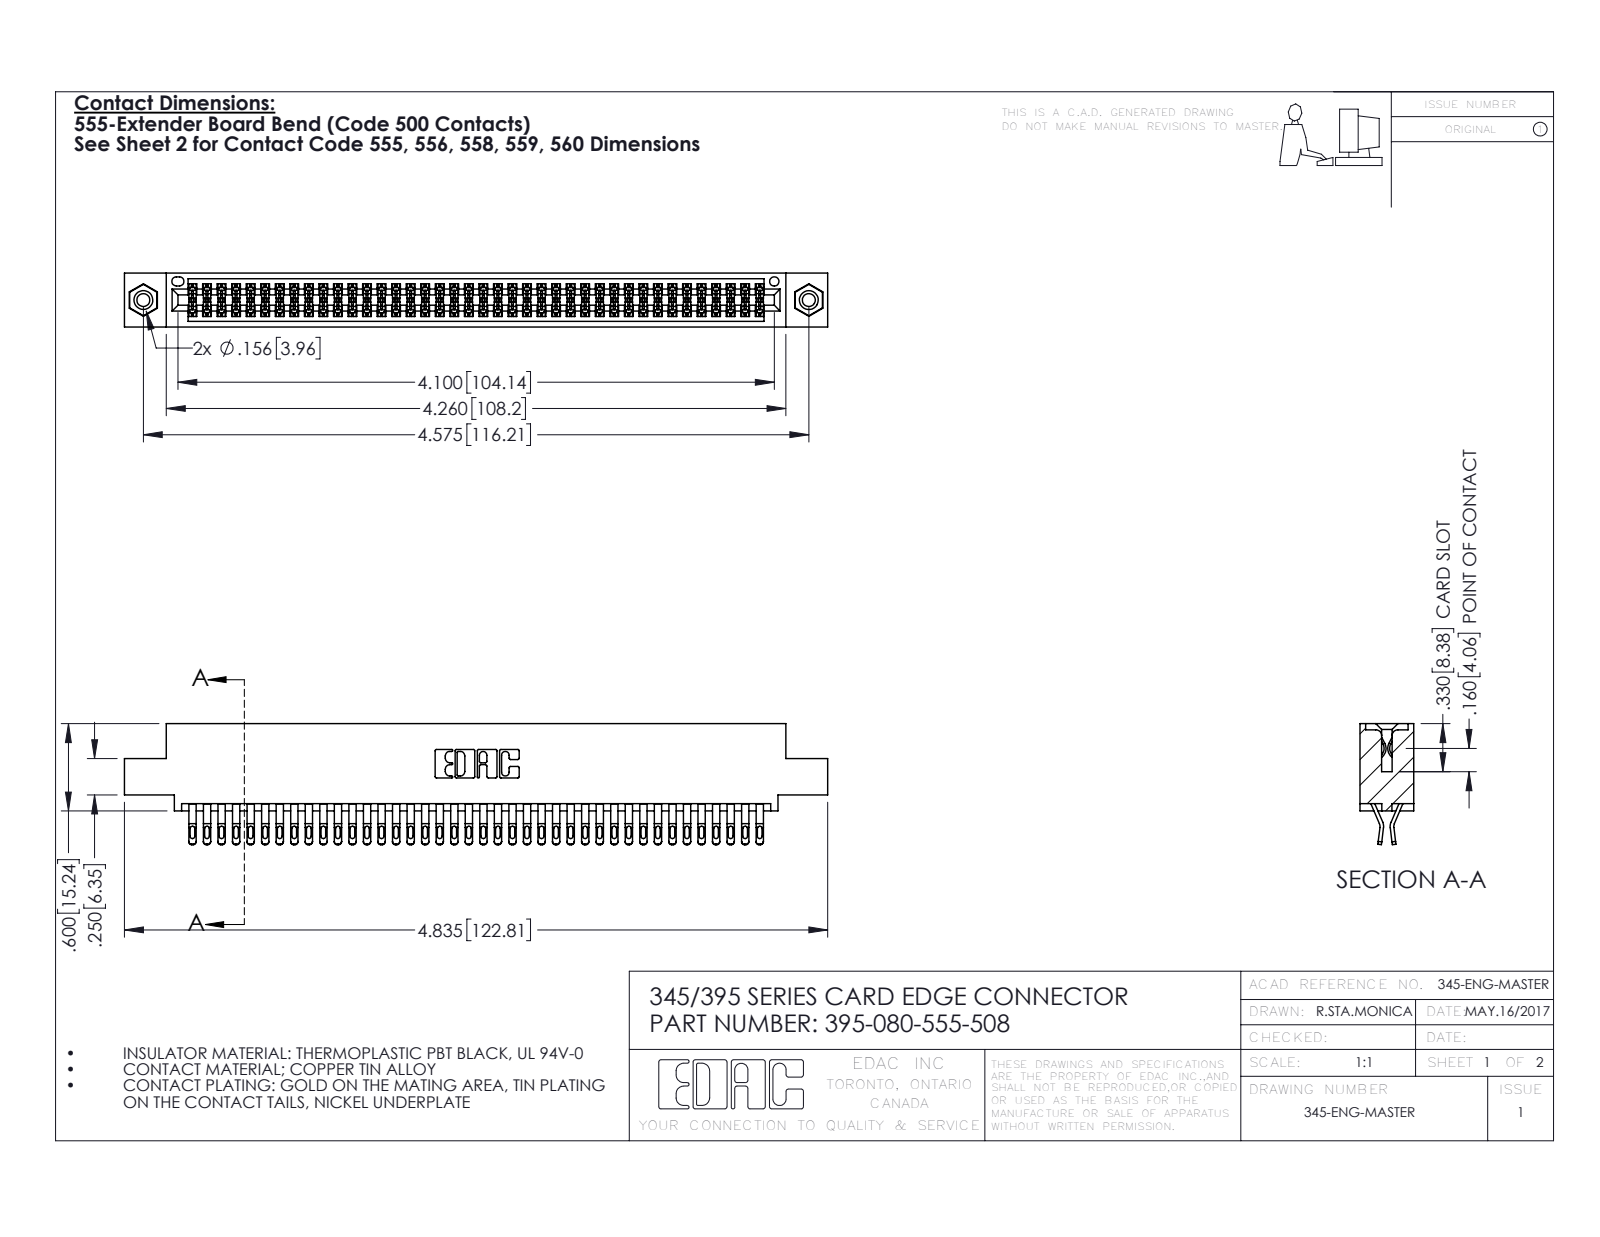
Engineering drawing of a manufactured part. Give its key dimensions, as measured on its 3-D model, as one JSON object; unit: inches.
{"part_name": "345-250-001_345-250-003-102; 345-292-001_555 Tail; 395-080-555-508; 345 Part_0.110 Offset - 0.156 Dia-TI", "step_written_by": "SolidWorks 2016 (CONFIG_CONTROL_DESIGN)", "units": "inches", "bodies": {"solids": 83, "faces": 4670, "planar": 2596, "cylindrical": 2058, "other": 16}, "overall_size": [4.835, 0.832, 0.37], "volume_in3": 0.736, "surface_area_in2": 28.99, "round_holes": [[0.089, 2], [0.125, 2], [0.156, 2], [0.064, 1]], "round_bosses_or_shafts": [[0.155, 2]], "partial_cylinders_radius": [[0.016, 200], [0.02, 160], [0.006, 120], [0.01, 22], [0.007, 6], [0.031, 6], [0.026, 3], [0.01, 2]], "face_to_face_distances": [0.072, 0.298, 0.025, 0.37, 0.2, 0.098, 0.272, 0.225, 0.175, 0.149], "hole_center_spacings": [0.27, 4.339, 4.575]}
